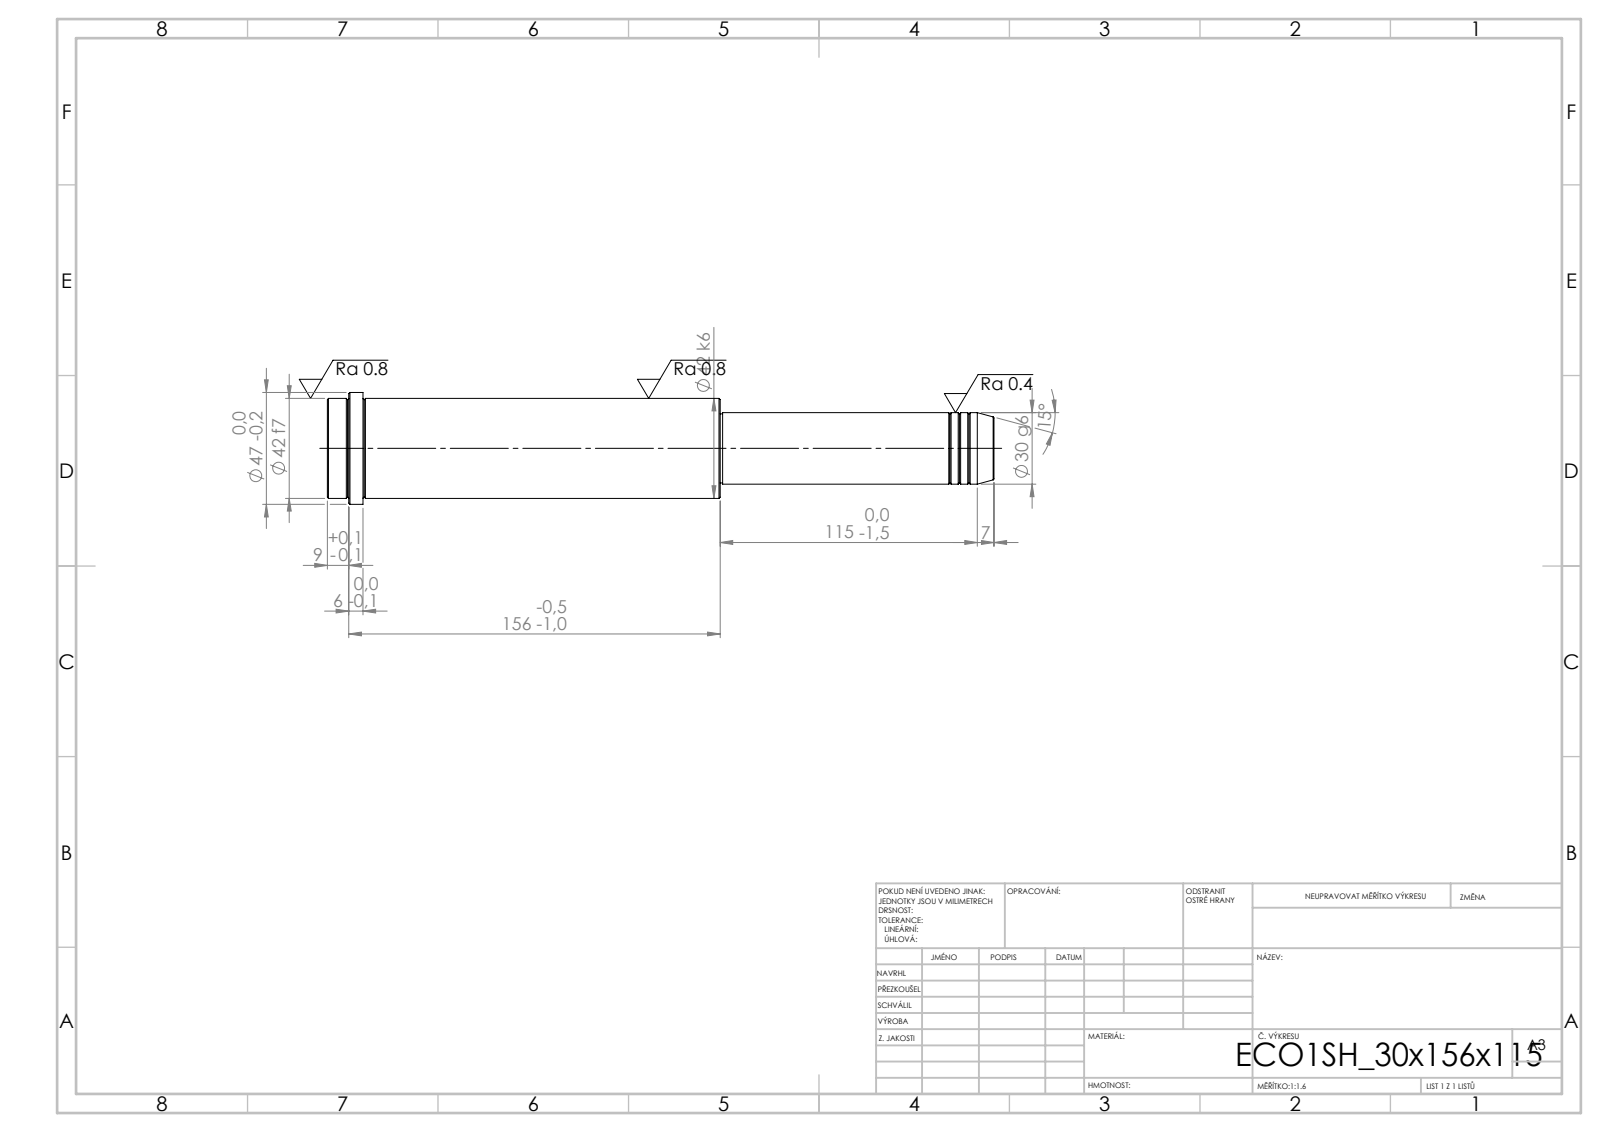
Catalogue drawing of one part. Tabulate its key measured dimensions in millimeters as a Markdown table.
| quantity | value |
| --- | --- |
| STEP written by | SolidWorks 2019 (CONFIG_CONTROL_DESIGN) |
| units | millimeters |
| bodies | 1 solid, 52 faces (6 planar, 16 cylindrical, 30 other) |
| overall size | 280 × 47 × 47 |
| volume | 311 079 mm³ |
| surface area | 36 244 mm² |
| round bosses / shafts (diameter × count) | 47 × 1, 42 × 1, 30 × 1, 29 × 1 |
| main face-to-face distances | 165, 115, 280, 265, 150, 15, 271, 156, 6, 9 |
